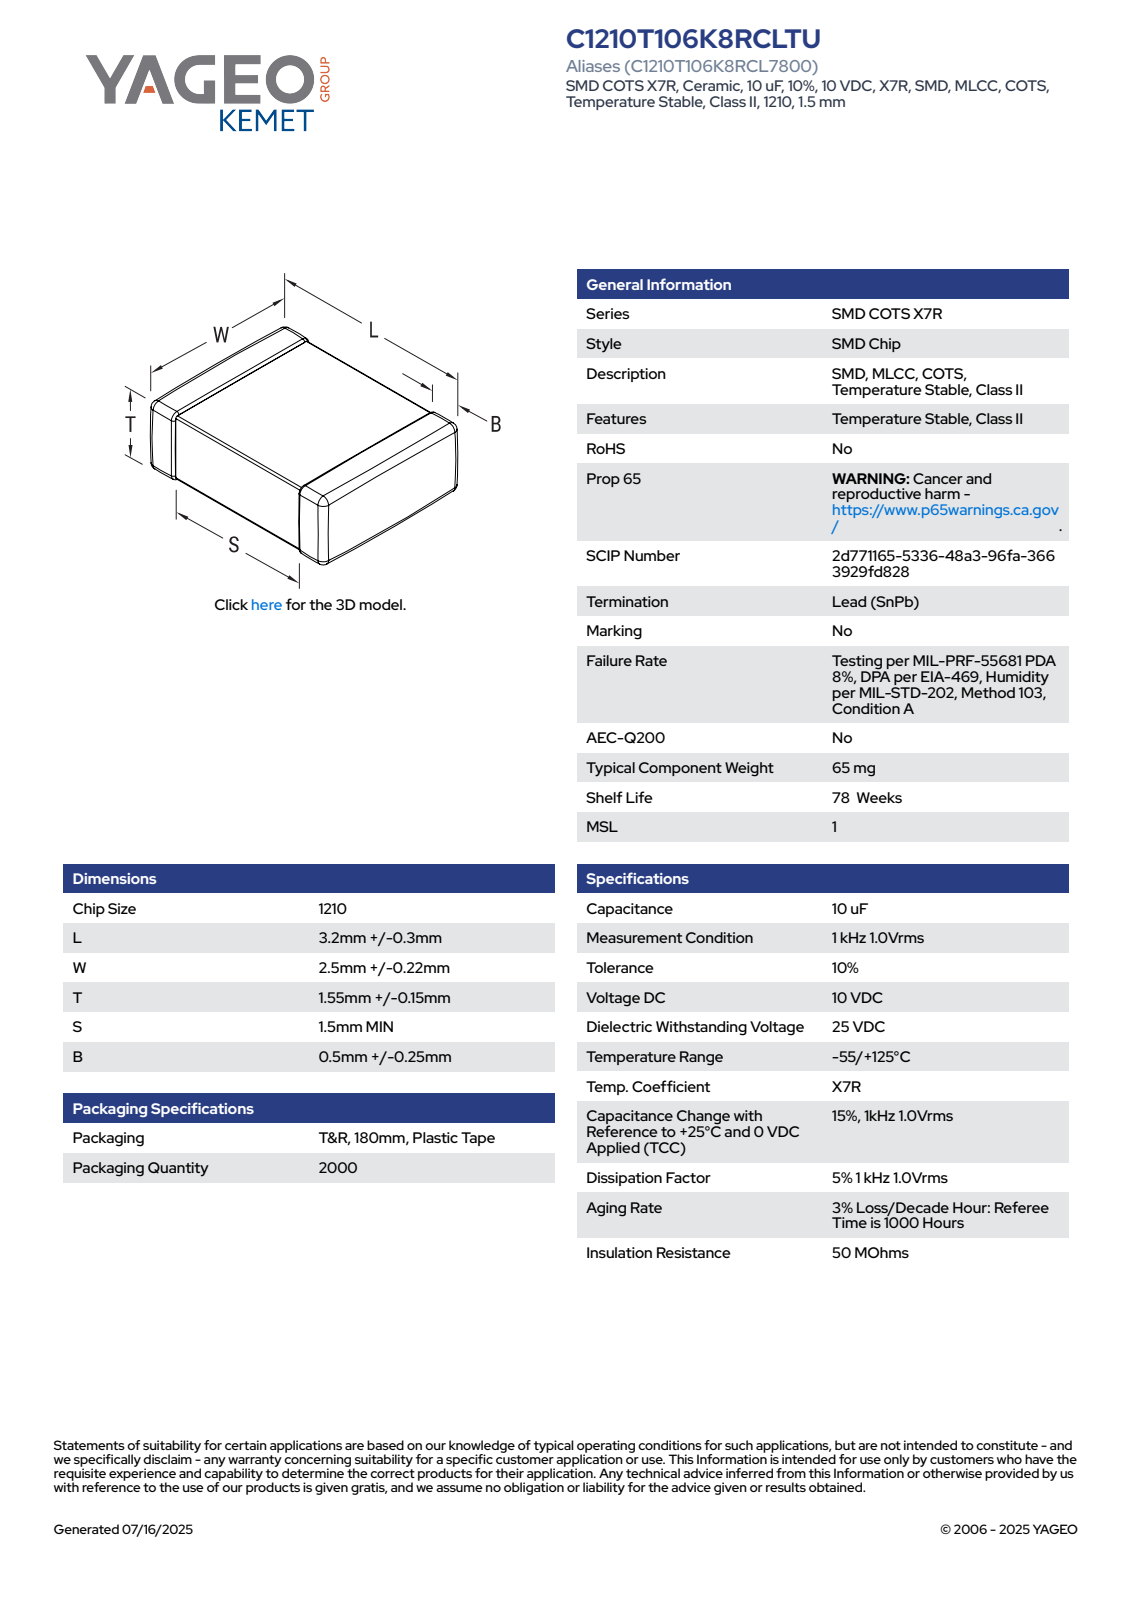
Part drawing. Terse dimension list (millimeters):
name: CCSM_STD_1210_L3.5W2.72T1.7S1.55B0.75
written by: SolidWorks 2021 (AUTOMOTIVE_DESIGN)
unit: mm
bodies: 4 solids, 125 faces (71 planar, 38 cylindrical, 16 other)
size: 3.5 × 2.72 × 1.7
volume: 15 mm³; area: 40 mm²
face distances: 1.64, 1.58, 3.5, 2.66, 1.7, 2.6, 2.72, 1.65, 1.59, 1.49
